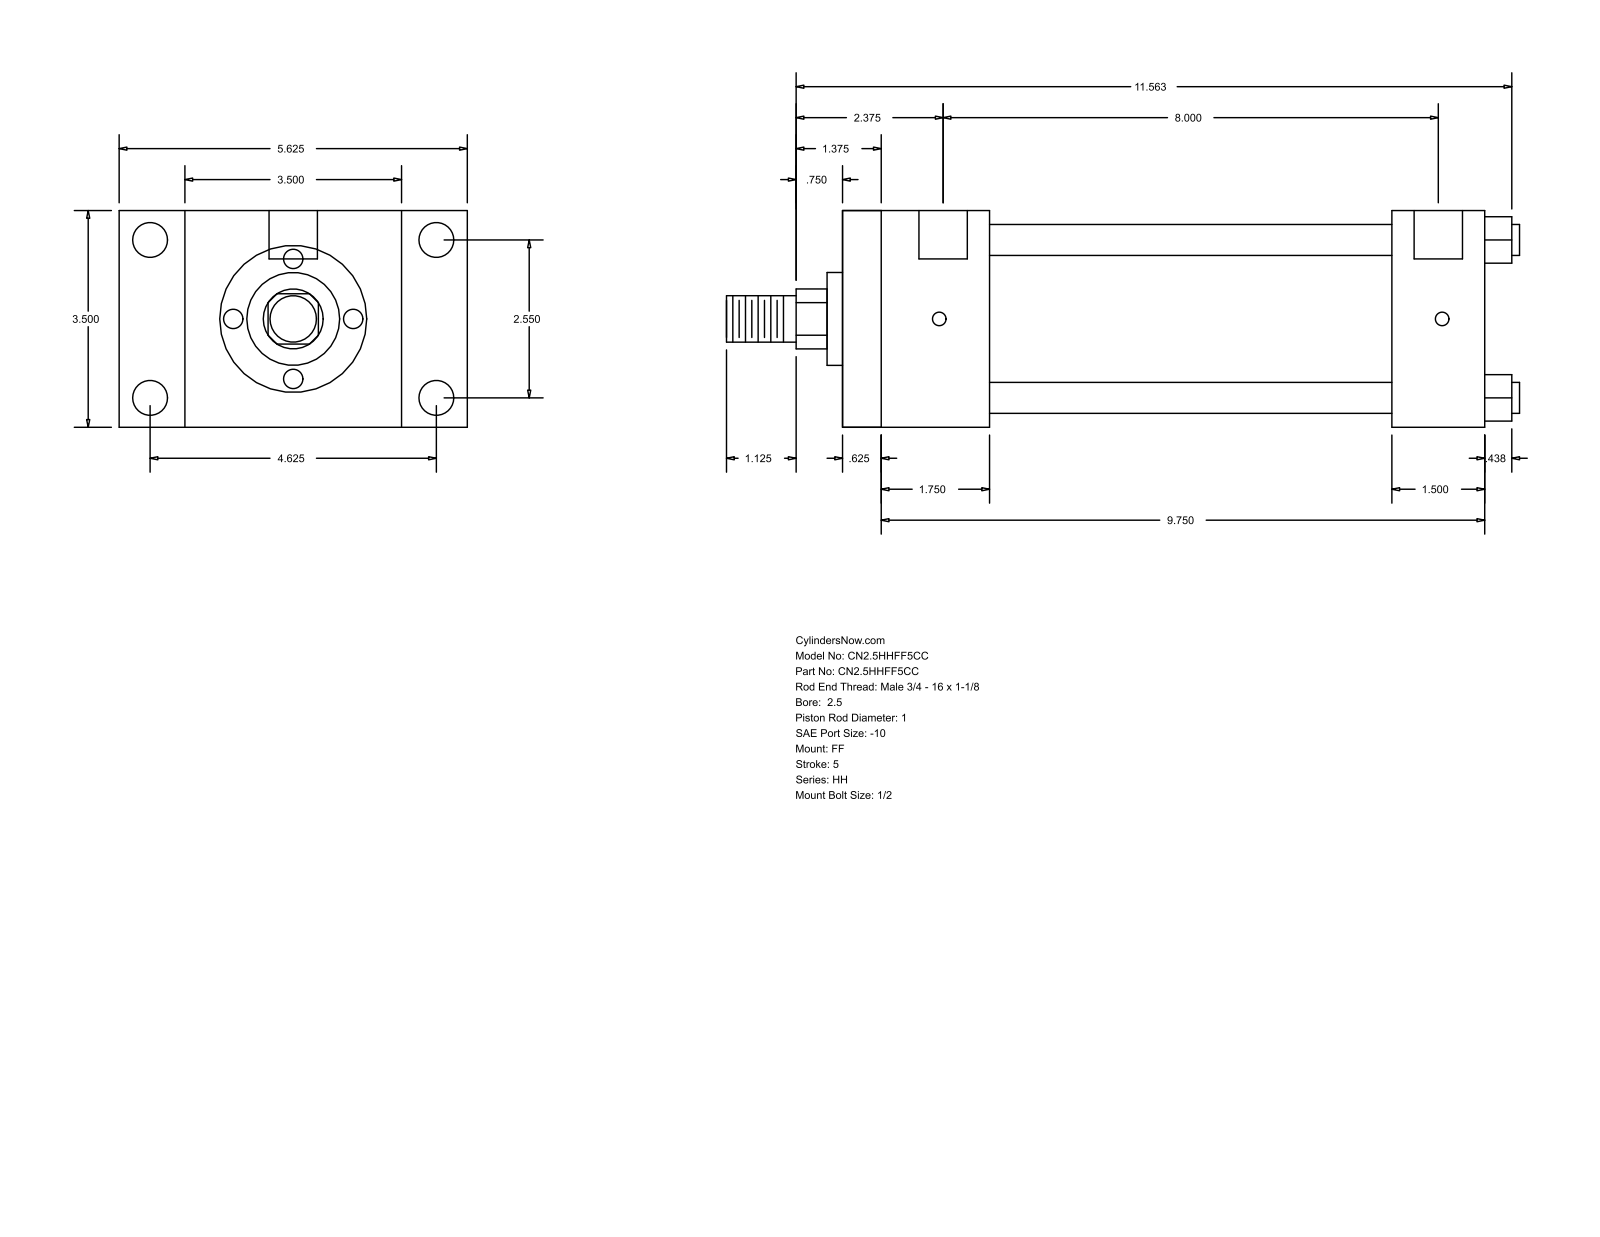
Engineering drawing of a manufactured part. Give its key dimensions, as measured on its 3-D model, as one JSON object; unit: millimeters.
{"part_name": "HH_FF__0250_1", "step_written_by": "GSSL Pune (CONFIG_CONTROL_DESIGN)", "units": "millimeters", "bodies": {"solids": 0, "faces": 92, "planar": 64, "cylindrical": 28, "other": 0}, "overall_size": [325.44, 142.88, 88.9], "round_holes": [[5.56, 4], [14.3, 4], [19.84, 2]], "round_bosses_or_shafts": [[12.7, 4], [73.03, 1], [38.1, 1], [25.4, 1], [19.05, 1]], "partial_cylinders_radius": [[12.29, 1]], "face_to_face_distances": [88.9, 263.52, 15.87, 247.65, 38.1, 60.33, 44.46, 203.19, 225.42, 209.55], "hole_center_spacings": [1.59, 64.76, 117.48, 134.15, 204.78, 206.37, 203.19]}
